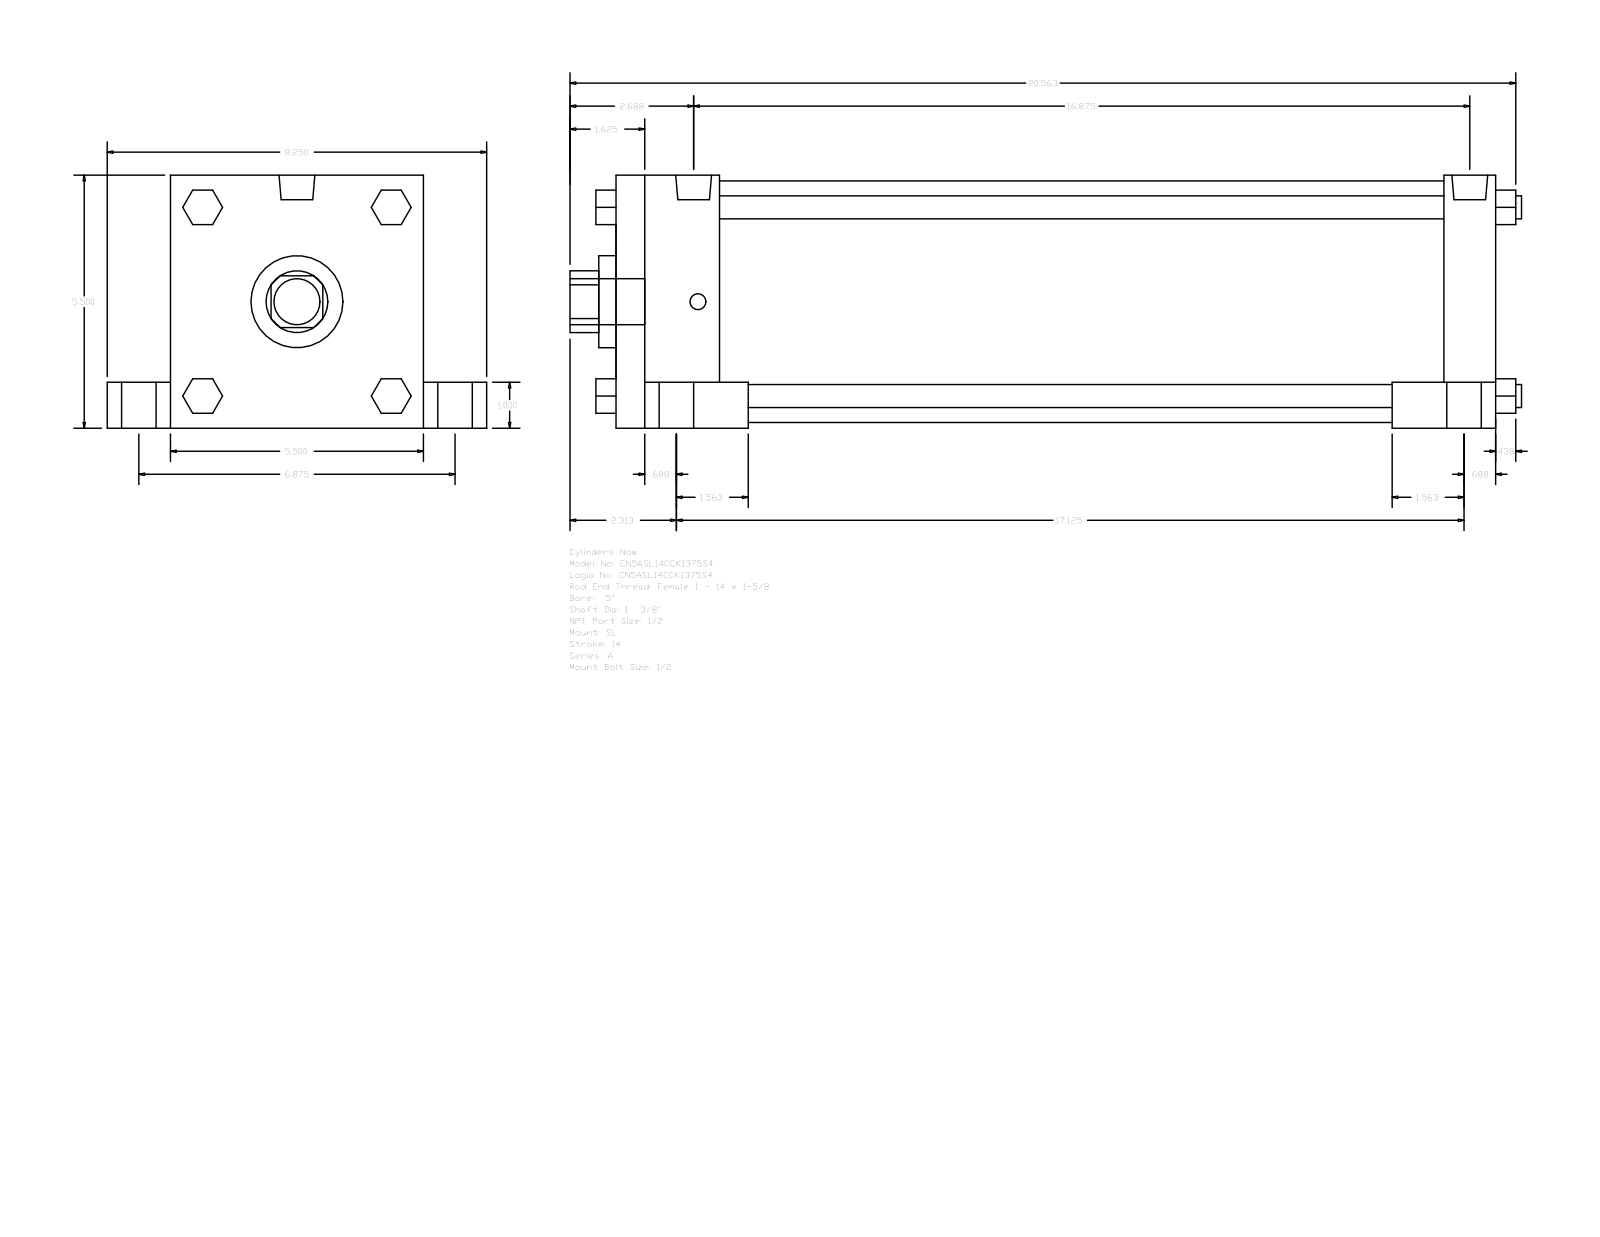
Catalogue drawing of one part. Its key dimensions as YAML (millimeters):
part_name: "A_SL__0500_1.375"
step_written_by: "GSSL Pune (CONFIG_CONTROL_DESIGN)"
units: millimeters
bodies: {solids: 0, faces: 150, planar: 114, cylindrical: 36, other: 0}
overall_size: [525.46, 209.55, 139.7]
round_holes:
  - {diameter: 34.92, count: 1}
  - {diameter: 50.8, count: 1}
  - {diameter: 133.35, count: 1}
round_bosses_or_shafts:
  - {diameter: 25.4, count: 5}
  - {diameter: 19.05, count: 4}
  - {diameter: 12.7, count: 4}
  - {diameter: 8.73, count: 4}
  - {diameter: 19.77, count: 2}
partial_cylinders:
  - {radius: 17.06, count: 1}
face_to_face_distances: [139.7, 485.78, 28.58, 57.15, 25.4, 114.3, 34.93, 174.63, 457.2, 400.05]
